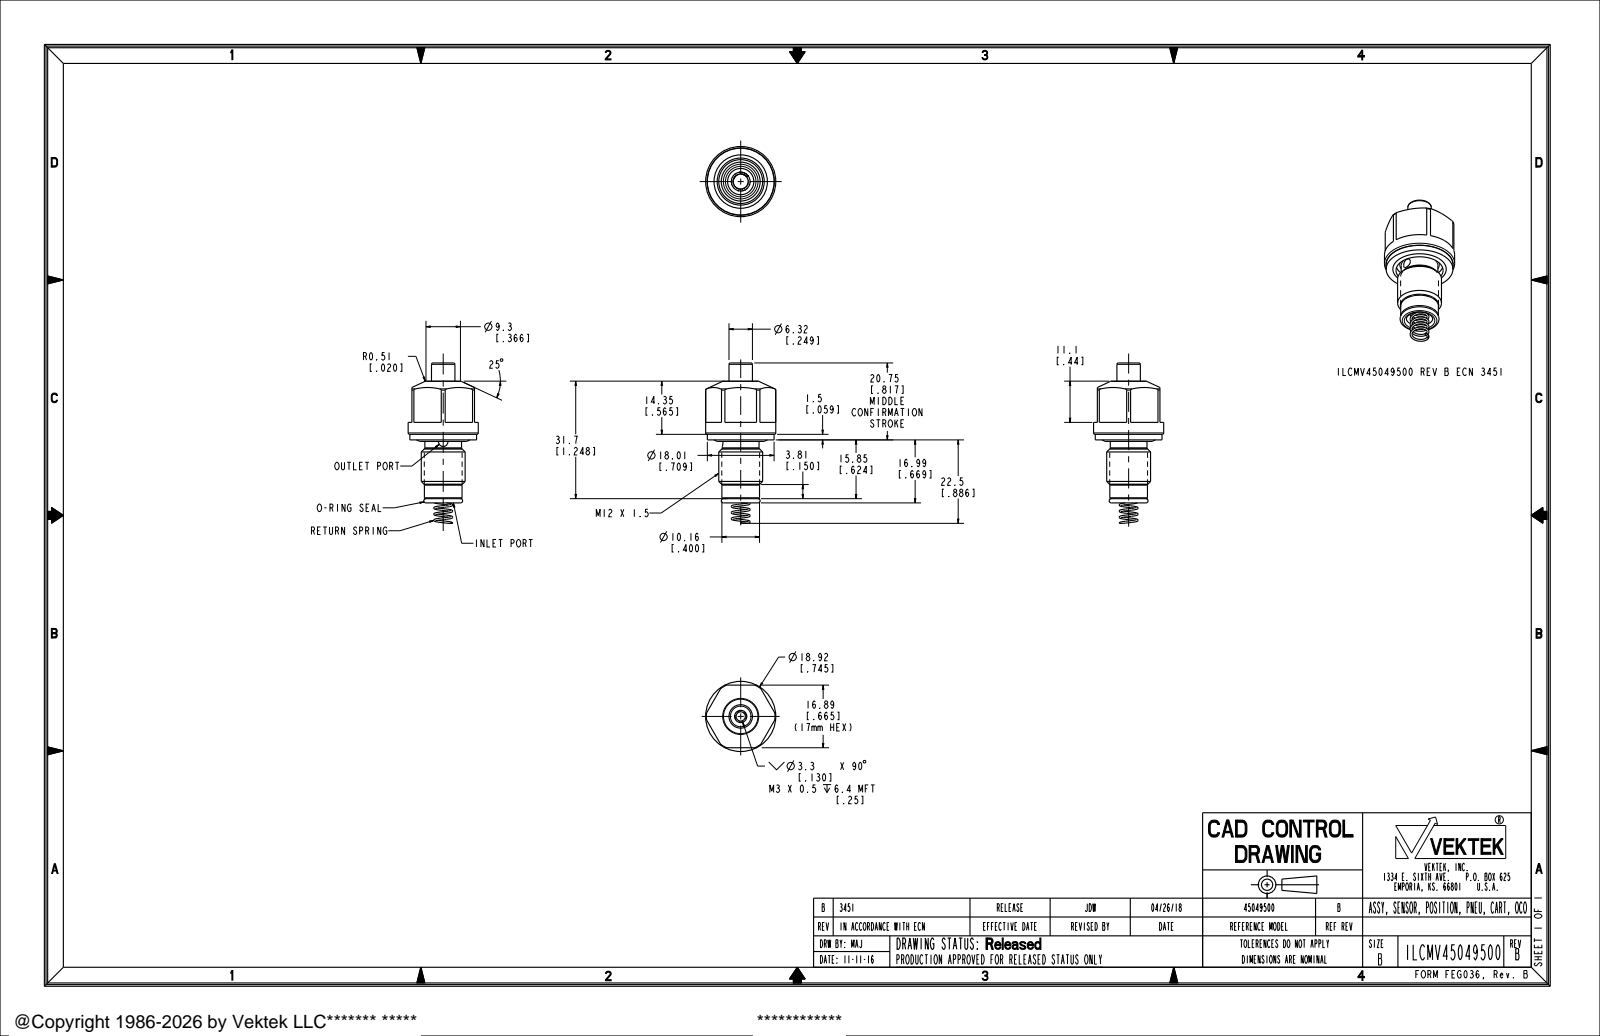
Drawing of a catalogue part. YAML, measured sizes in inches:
part_name: "ILCMV45049500"
step_written_by: "PRO/ENGINEER BY PARAMETRIC TECHNOLOGY CORPORATION, 2013320 (AUTOMOTIVE_DESIGN)"
units: inches
bodies: {solids: 1, faces: 92, planar: 26, cylindrical: 24, other: 42}
overall_size: [1.703, 0.745, 0.745]
volume: 0.31
surface_area: 4.867
round_holes:
  - {diameter: 0.098, count: 1}
  - {diameter: 0.1, count: 1}
  - {diameter: 0.118, count: 1}
  - {diameter: 0.312, count: 1}
  - {diameter: 0.5, count: 1}
round_bosses_or_shafts:
  - {diameter: 0.745, count: 1}
  - {diameter: 0.709, count: 1}
  - {diameter: 0.466, count: 1}
  - {diameter: 0.402, count: 1}
  - {diameter: 0.4, count: 1}
  - {diameter: 0.39, count: 1}
  - {diameter: 0.249, count: 1}
face_to_face_distances: [0.665, 0.324, 0.624, 0.383, 0.059, 0.948, 0.565, 0.51, 0.186, 0.127]
